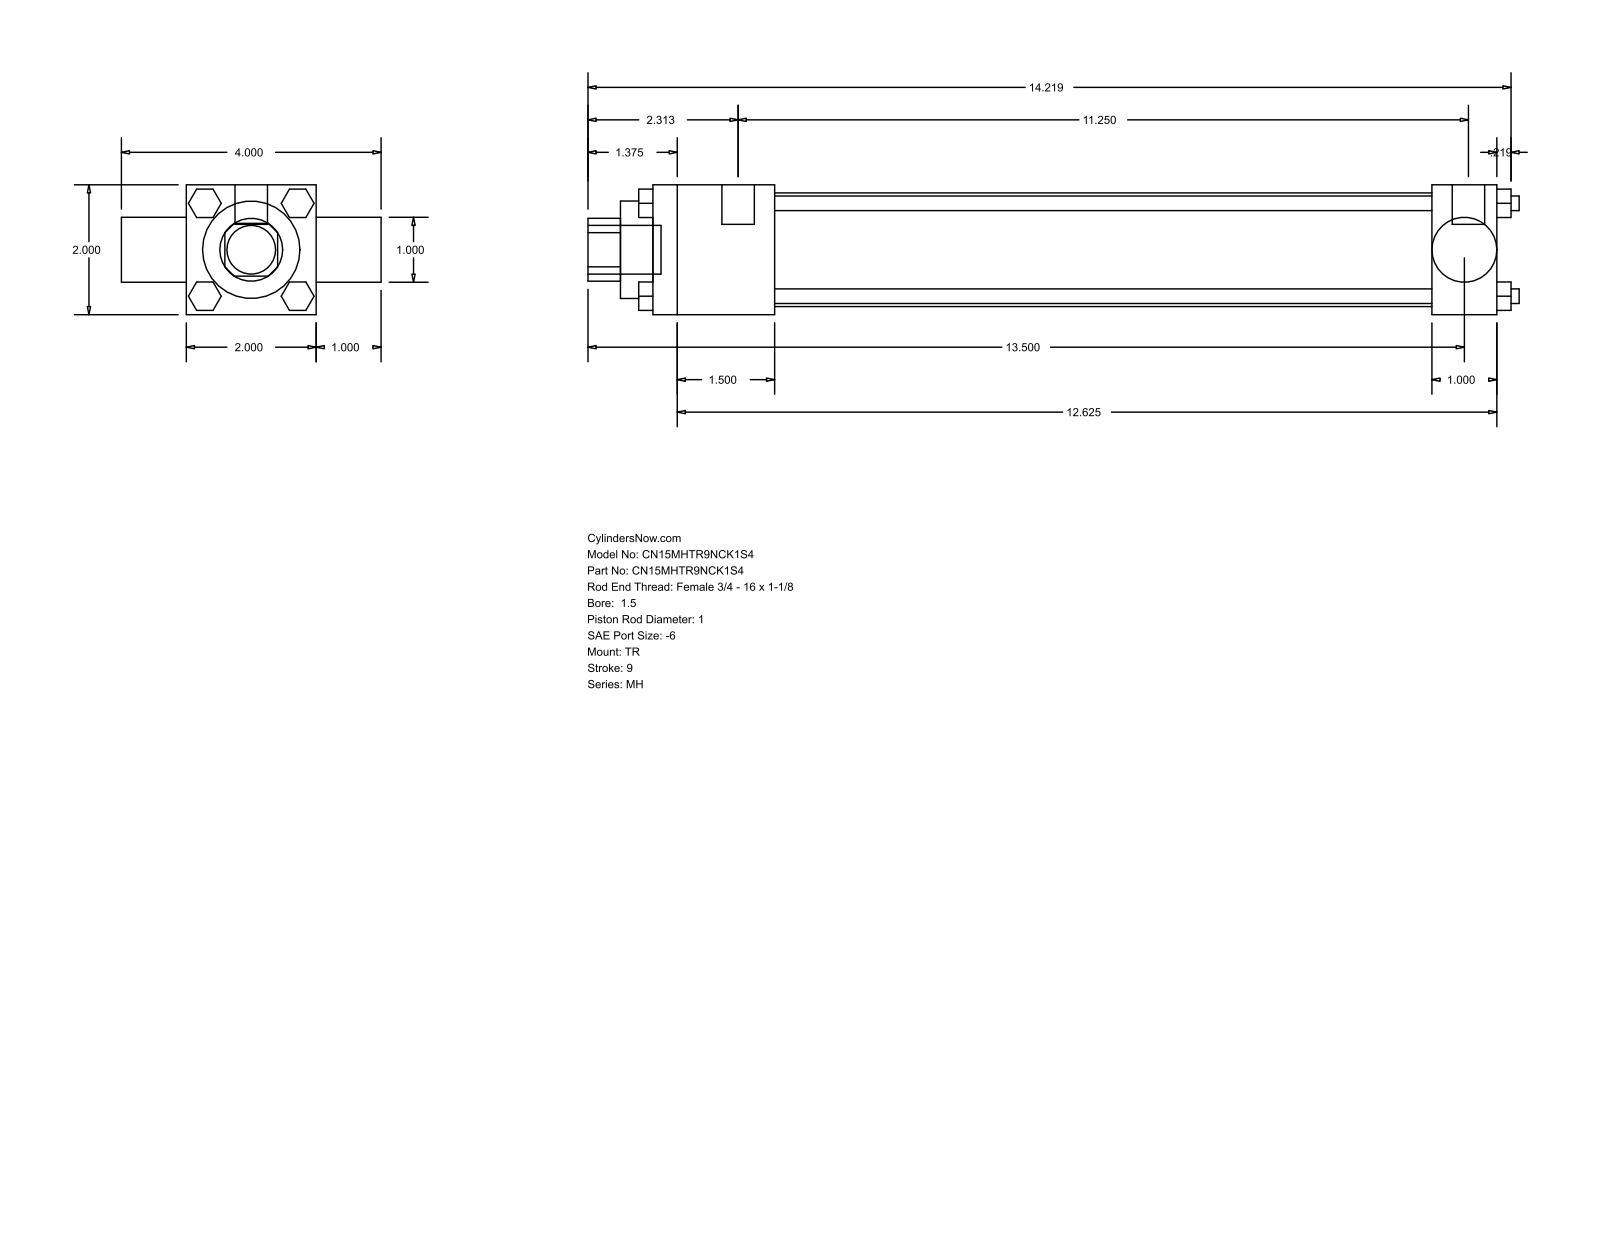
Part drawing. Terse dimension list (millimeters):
name: MH_TR__0150_1
written by: GSSL Pune (CONFIG_CONTROL_DESIGN)
unit: mm
bodies: 0 solids, 120 faces (92 planar, 28 cylindrical, 0 other)
size: 364.33 × 101.6 × 50.8
holes: 1× ⌀25.35, 1× ⌀25.4, 1× ⌀38.1, 1× ⌀44.45
bosses: 4× ⌀5.71, 3× ⌀5.56, 2× ⌀12.7, 1× ⌀19.05
rounds: 1× R12.29
face distances: 50.8, 25.4, 330.2, 76.2, 47.63, 282.57, 304.8, 257.17, 335.76, 12.7
